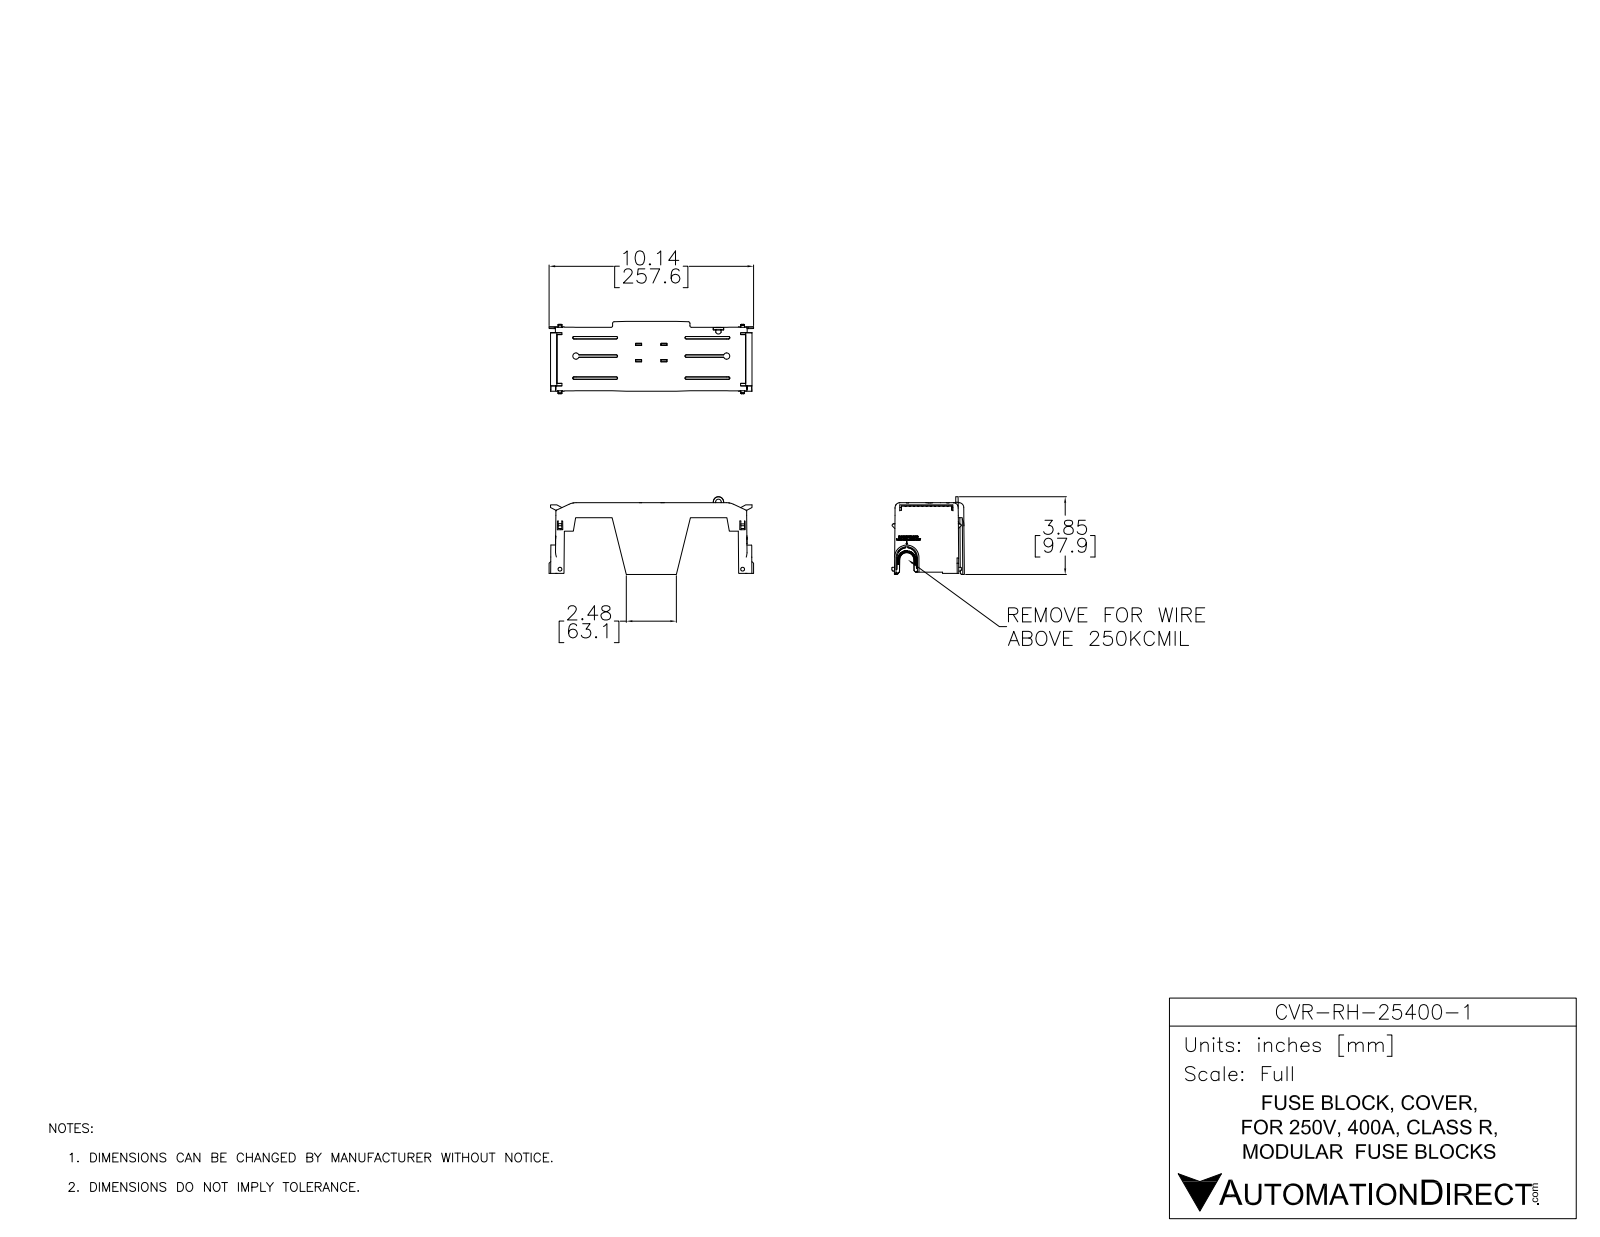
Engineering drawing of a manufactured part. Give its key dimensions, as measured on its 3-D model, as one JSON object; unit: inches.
{"part_name": "CVR-RH-25400-1", "step_written_by": "SolidWorks 2017 (AUTOMOTIVE_DESIGN)", "units": "inches", "bodies": {"solids": 1, "faces": 2380, "planar": 1598, "cylindrical": 106, "other": 676}, "overall_size": [10.143, 3.853, 3.593], "volume_in3": 7.778, "surface_area_in2": 207.6, "round_holes": [[0.276, 1]], "partial_cylinders_radius": [[0.039, 19], [0.118, 8], [0.157, 7], [0.236, 7], [0.079, 6], [0.01, 2], [0.02, 2], [0.232, 2]], "face_to_face_distances": [0.079, 0.276, 0.197, 0.354, 0.118, 0.669, 0.392, 1.338, 0.24, 1.098]}
